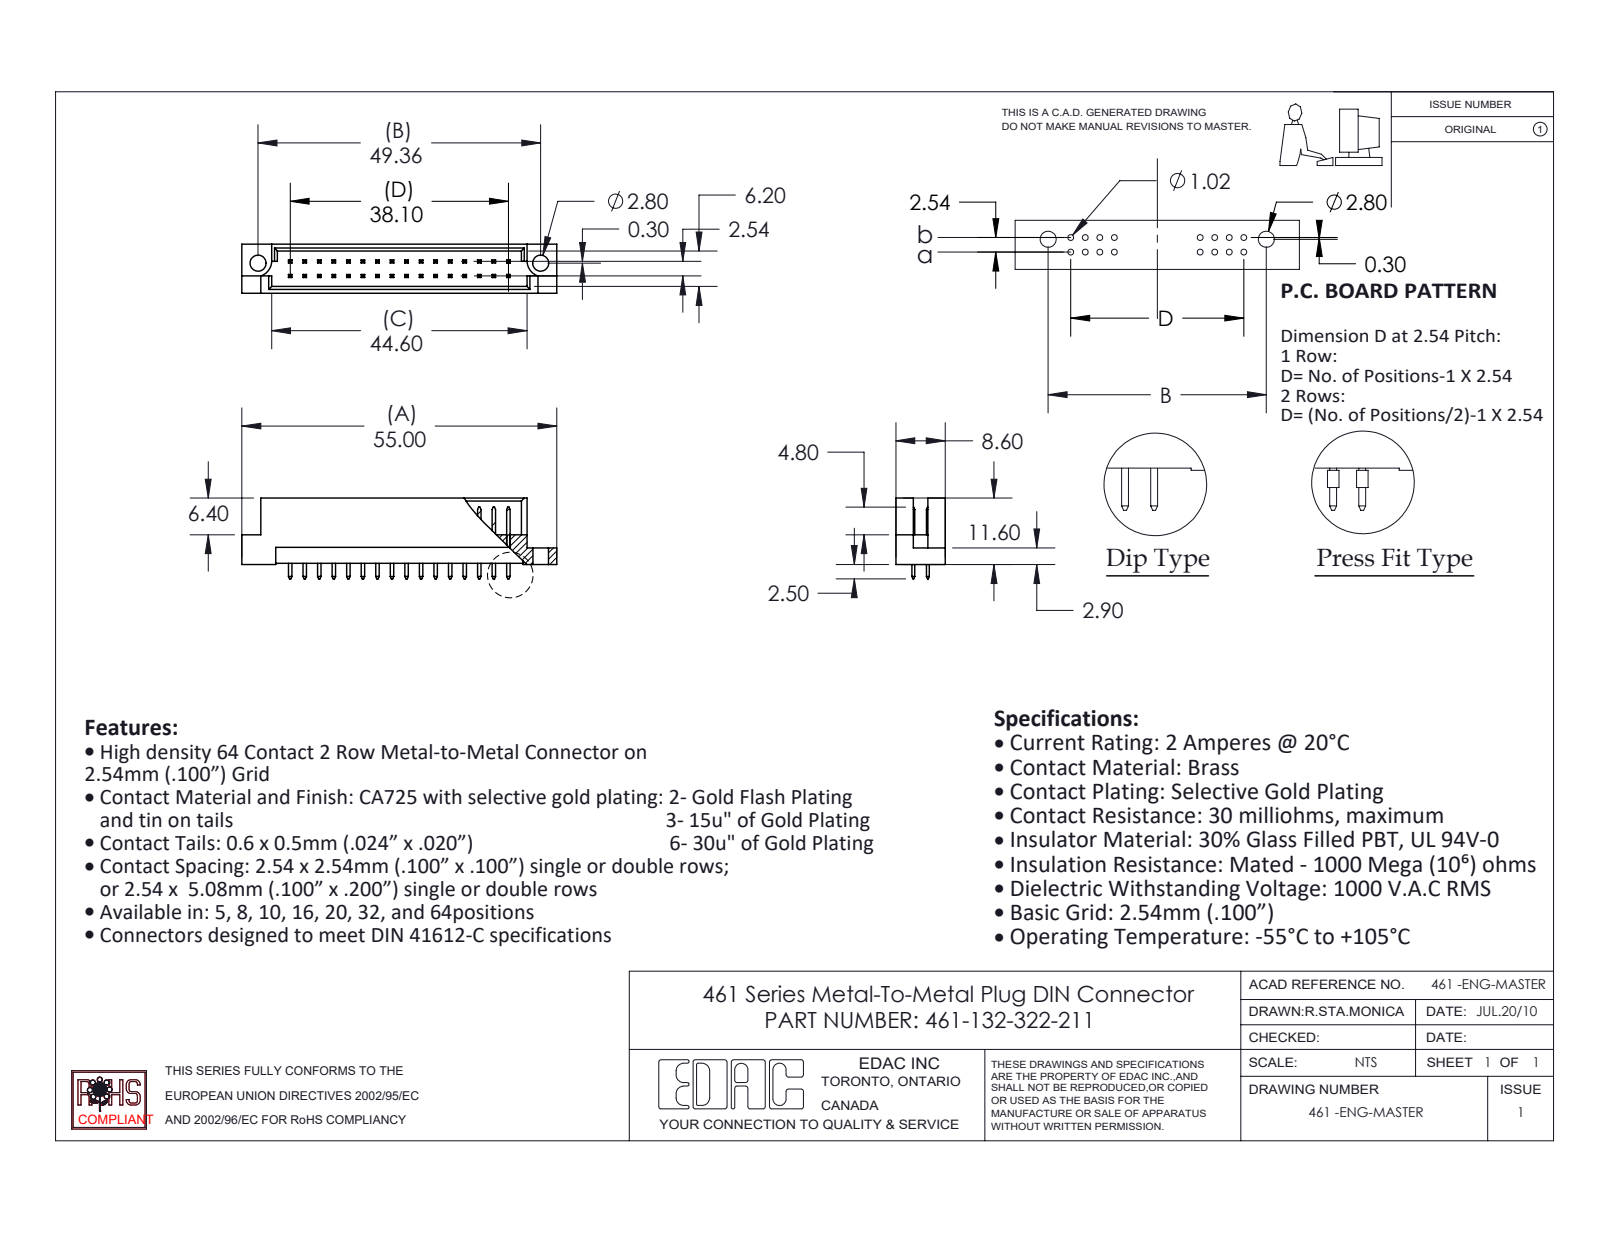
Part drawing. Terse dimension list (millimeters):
name: 461 Part_32; 461-132-322-211; 461-290_22
written by: SolidWorks 2020 (CONFIG_CONTROL_DESIGN)
unit: mm
bodies: 33 solids, 624 faces (618 planar, 6 cylindrical, 0 other)
size: 55 × 14.1 × 8.6
volume: 2 770 mm³; area: 4 115 mm²
holes: 2× ⌀2.8
rounds: 2× R2.8
face distances: 1.2, 7.4, 2.54, 8.6, 6.2, 2.78, 5.82, 1.58, 4.62, 3.28
hole spacings: 49.36
